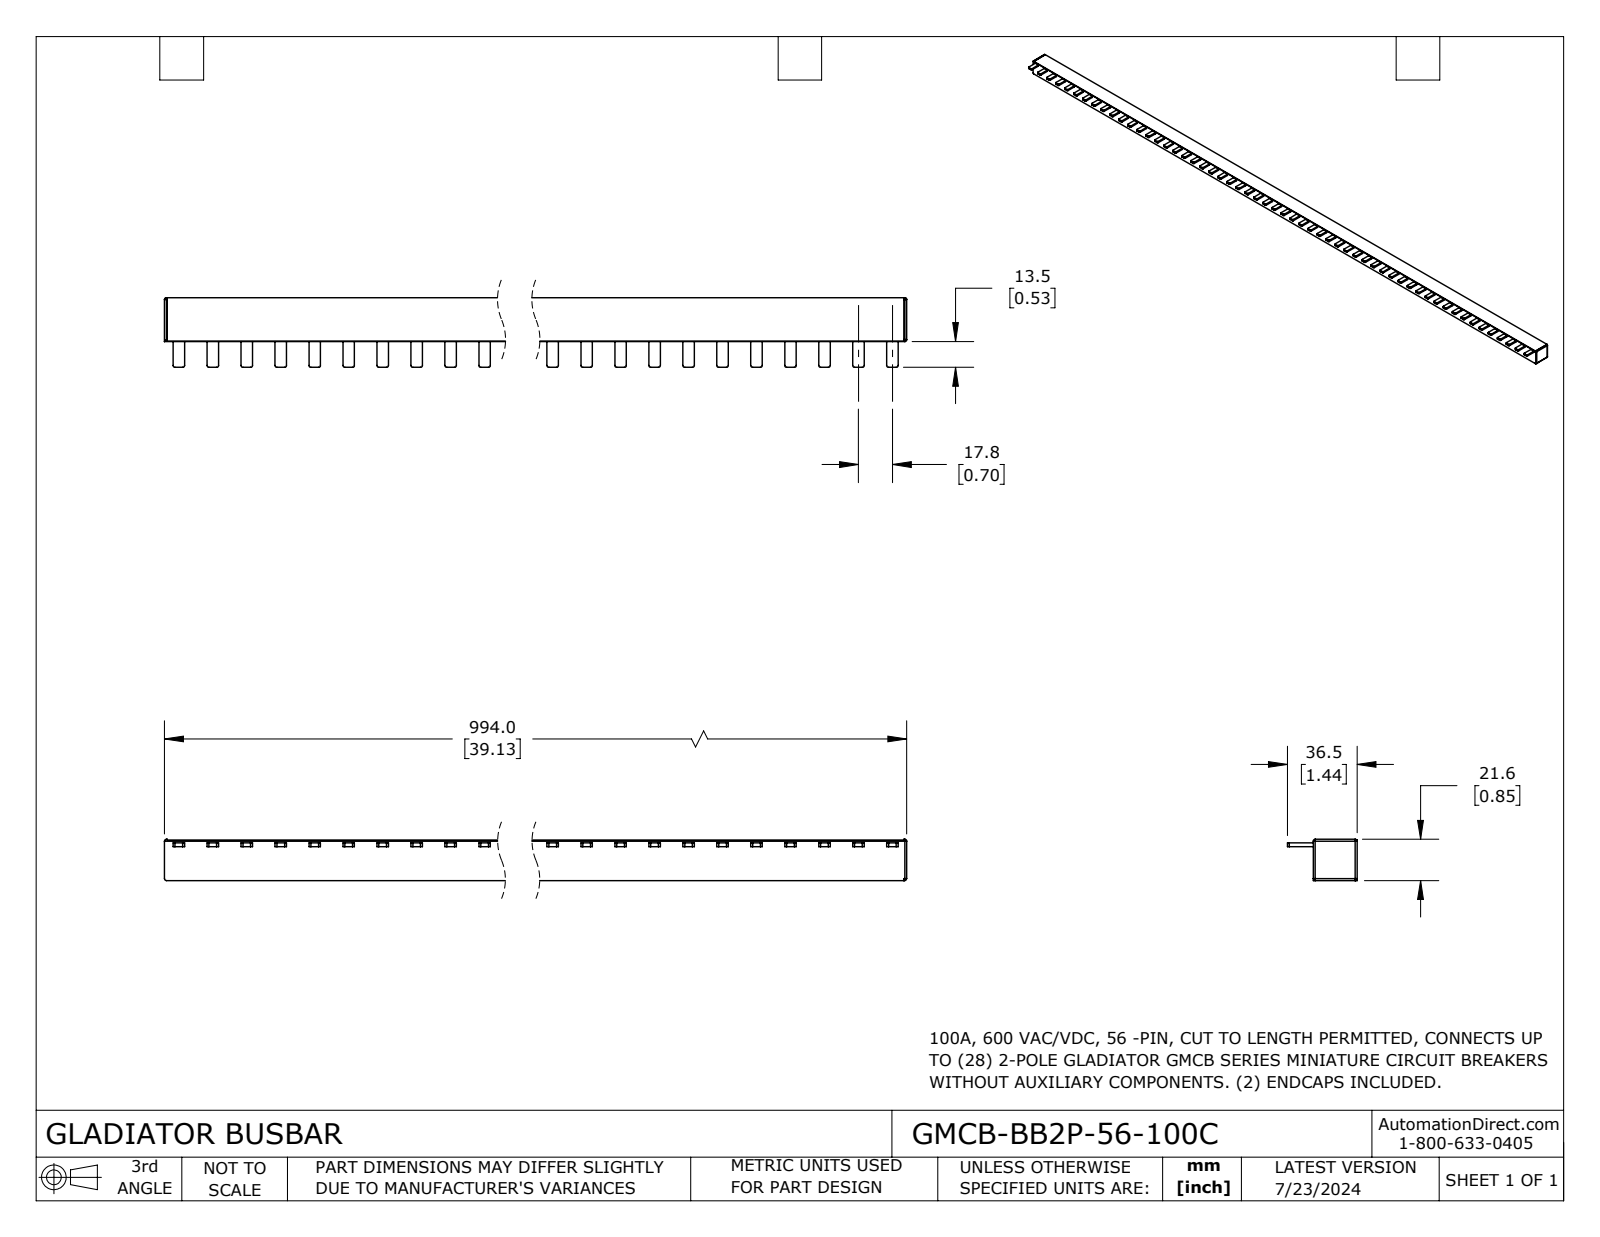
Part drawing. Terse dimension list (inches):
name: GMCB-BB2P-56-100C
written by: SolidWorks 2023 (CONFIG_CONTROL_DESIGN)
unit: in
bodies: 1 solid, 428 faces (295 planar, 125 cylindrical, 8 other)
size: 39.134 × 1.437 × 0.85
volume: 30.12 in³; area: 155.9 in²
rounds: 123× R0.039
face distances: 0.835, 0.906, 0.138, 0.697, 0.059, 0.079, 0.776, 1.437, 0.531, 39.134
